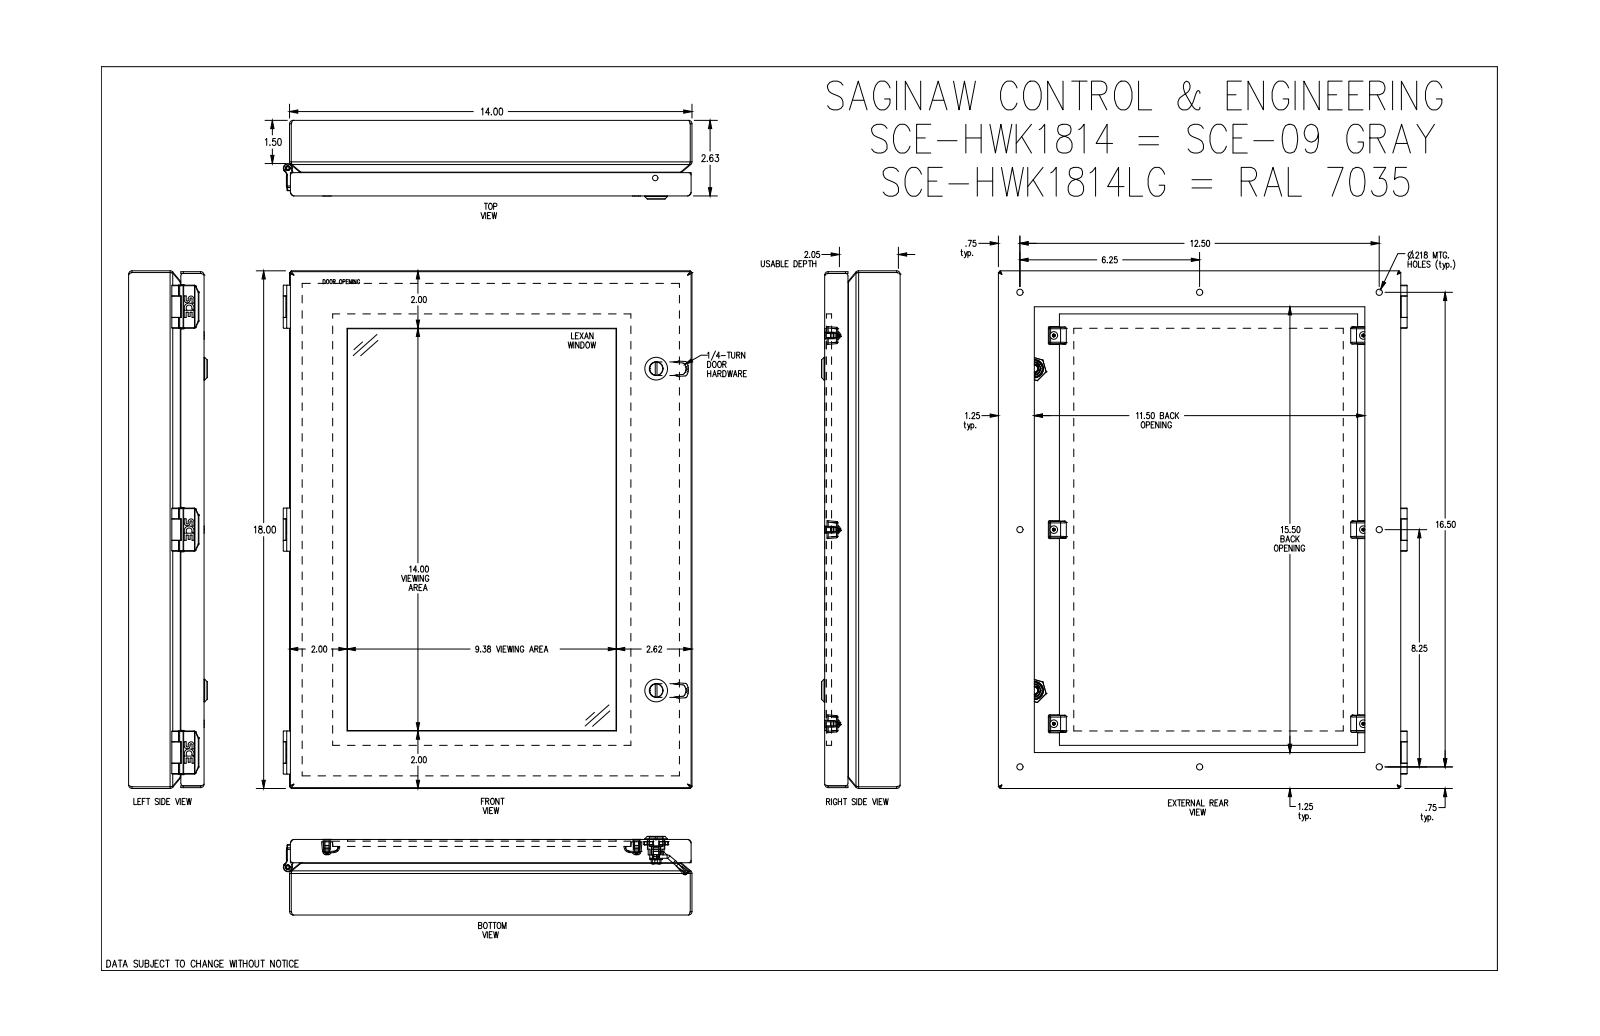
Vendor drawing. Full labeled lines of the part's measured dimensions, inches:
Part name (STEP PRODUCT): SCE-HWK1814
STEP written by: SolidWorks 2021 (AUTOMOTIVE_DESIGN)
Units: inches
Bodies: 54 solids, 2831 faces (1164 planar, 773 cylindrical, 894 other)
Overall size (bounding box): 18.06 × 14.22 × 2.733
Volume: 88.04 in³ · Surface area: 2 034 in²
Round holes (diameter × count): ⌀0.138 ×6, ⌀0.156 ×6, ⌀0.213 ×6, ⌀0.218 ×6, ⌀0.164 ×3, ⌀0.17 ×3, ⌀0.174 ×3, ⌀0.266 ×3, ⌀0.338 ×3, ⌀0.2 ×2, ⌀0.239 ×2, ⌀0.254 ×2
Round bosses / shafts (diameter × count): ⌀0.262 ×6, ⌀0.212 ×6, ⌀0.479 ×3, ⌀0.26 ×3, ⌀0.15 ×3, ⌀0.788 ×2, ⌀0.548 ×2, ⌀0.46 ×2
Partial cylindrical surfaces — rounded edges, fillets, slot ends (radius × count): R0.106 ×99, R0.005 ×54, R0.008 ×48, R0.02 ×44, R0.05 ×36, R0.025 ×18, R0.01 ×16, R0.06 ×16
Main face-to-face distances: 0.059, 0.06, 0.181, 0.241, 2.385, 2.566, 2.626, 0.236, 2.621, 0.055
Hole centre spacings: 6.75, 7.75, 8.276, 12.711, 15.035, 10.77, 12.552, 1.34
